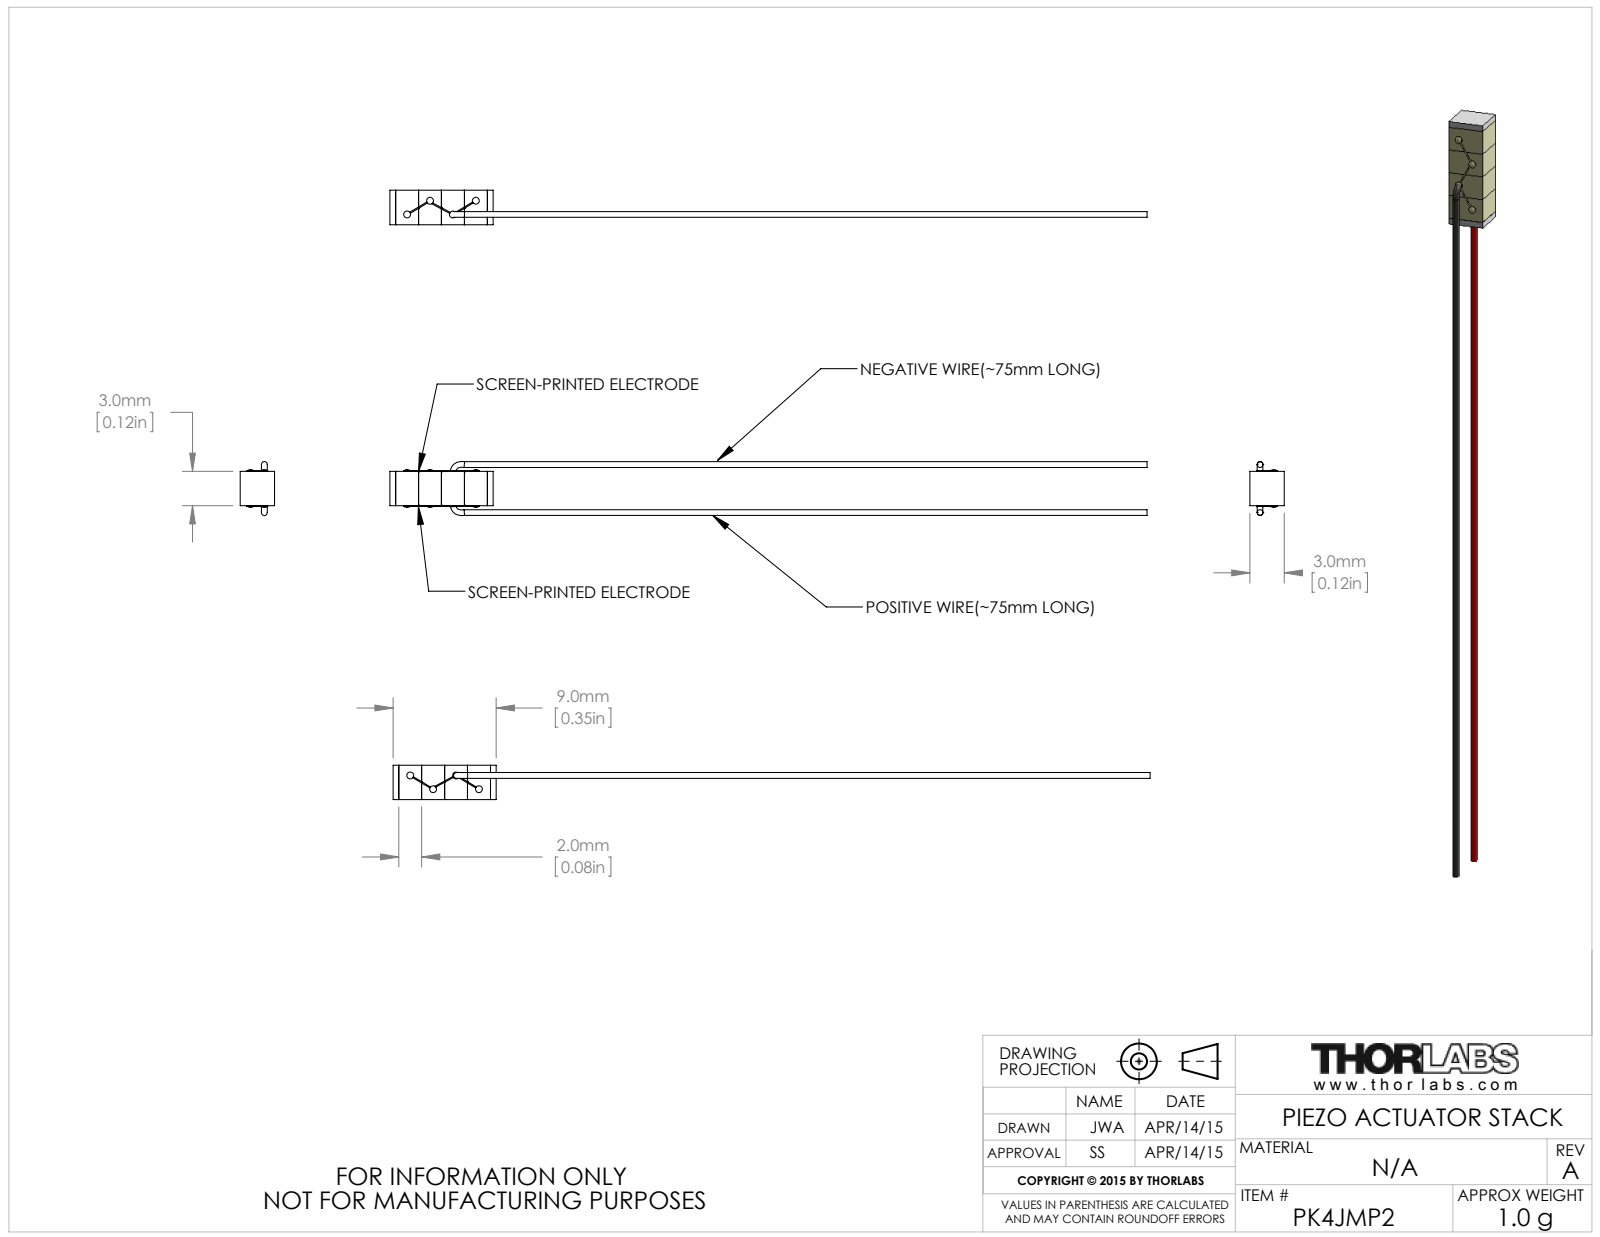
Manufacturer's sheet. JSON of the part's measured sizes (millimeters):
{"part_name": "CTN003042", "step_written_by": "SolidWorks 2014 (AUTOMOTIVE_DESIGN)", "units": "millimeters", "bodies": {"solids": 4, "faces": 103, "planar": 43, "cylindrical": 36, "other": 24}, "overall_size": [66.1, 4.72, 3], "volume_mm3": 105, "surface_area_mm2": 410, "round_bosses_or_shafts": [[0.6, 4]], "face_to_face_distances": [2, 3, 4, 6, 0.5, 8.51, 2.51, 4.51, 6.51, 2.01]}
